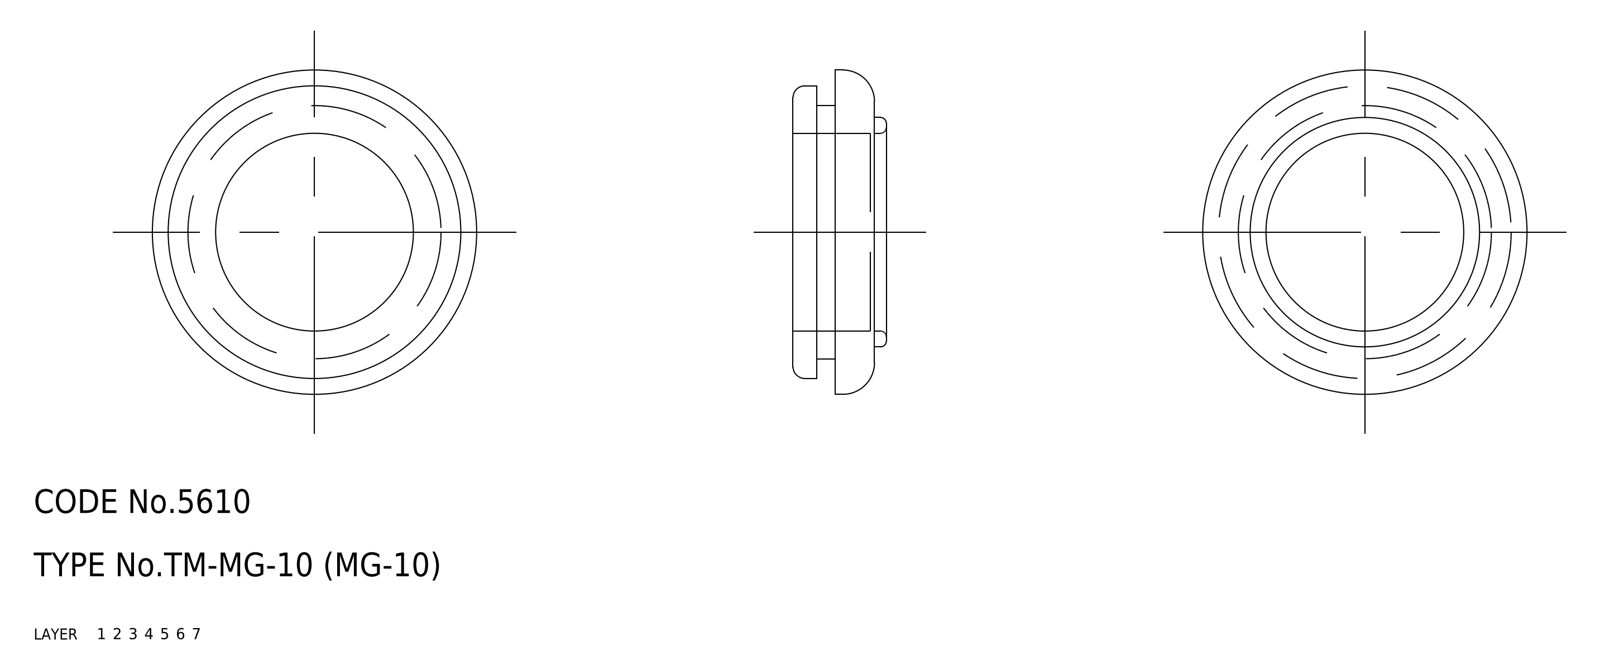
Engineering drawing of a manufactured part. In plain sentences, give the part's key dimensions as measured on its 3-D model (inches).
The part is named "grommet". Its 3-D file was written by "CADfix (AUTOMOTIVE_DESIGN)". It is 1 solid with 27 faces: 0 planar, 0 cylindrical and 27 other. Overall it measures 1.614 by 1.614 by 0.465 inches. Its volume is 0.405 cubic inches and its surface area 7.865 square inches.
